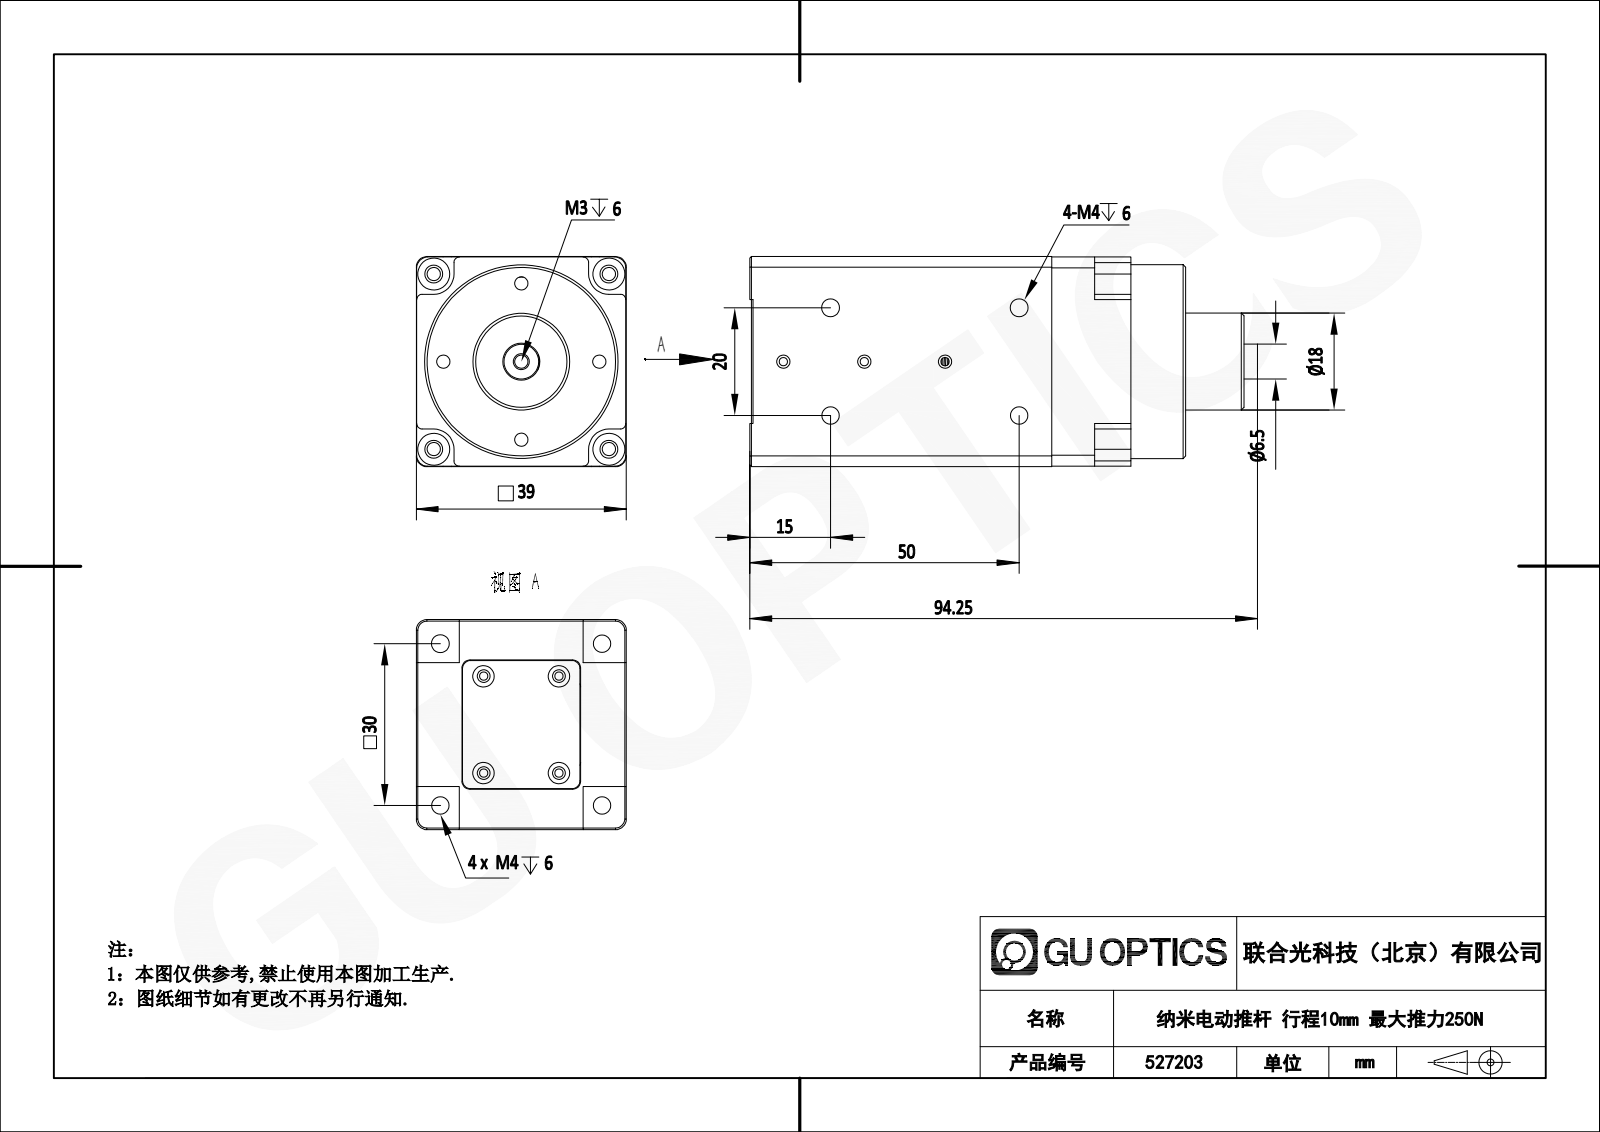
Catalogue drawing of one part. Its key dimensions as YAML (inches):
part_name: "527203"
step_written_by: "SolidWorks 2020 (AUTOMOTIVE_DESIGN)"
units: inches
bodies: {solids: 7, faces: 480, planar: 210, cylindrical: 216, other: 54}
overall_size: [3.711, 1.535, 1.535]
volume: 6.333
surface_area: 62.29
round_holes:
  - {diameter: 0.098, count: 17}
  - {diameter: 0.13, count: 8}
  - {diameter: 0.134, count: 8}
  - {diameter: 0.063, count: 4}
  - {diameter: 0.081, count: 4}
  - {diameter: 0.094, count: 4}
  - {diameter: 0.106, count: 4}
  - {diameter: 0.157, count: 4}
  - {diameter: 0.177, count: 4}
  - {diameter: 0.236, count: 4}
  - {diameter: 0.244, count: 4}
  - {diameter: 0.049, count: 2}
round_bosses_or_shafts:
  - {diameter: 0.709, count: 1}
  - {diameter: 0.315, count: 1}
  - {diameter: 0.256, count: 1}
partial_cylinders:
  - {radius: 0.059, count: 44}
  - {radius: 0.02, count: 16}
  - {radius: 0.079, count: 11}
  - {radius: 0.039, count: 9}
  - {radius: 0.148, count: 4}
  - {radius: 0.177, count: 3}
  - {radius: 0.012, count: 2}
  - {radius: 0.031, count: 2}
face_to_face_distances: [1.457, 1.531, 0.071, 1.528, 0.193, 1.339, 0.067, 1.386, 0.063, 0.197]
hole_center_spacings: [0.591, 0.643, 1.231, 1.303, 1.369, 0.898, 0.394, 0.996]
